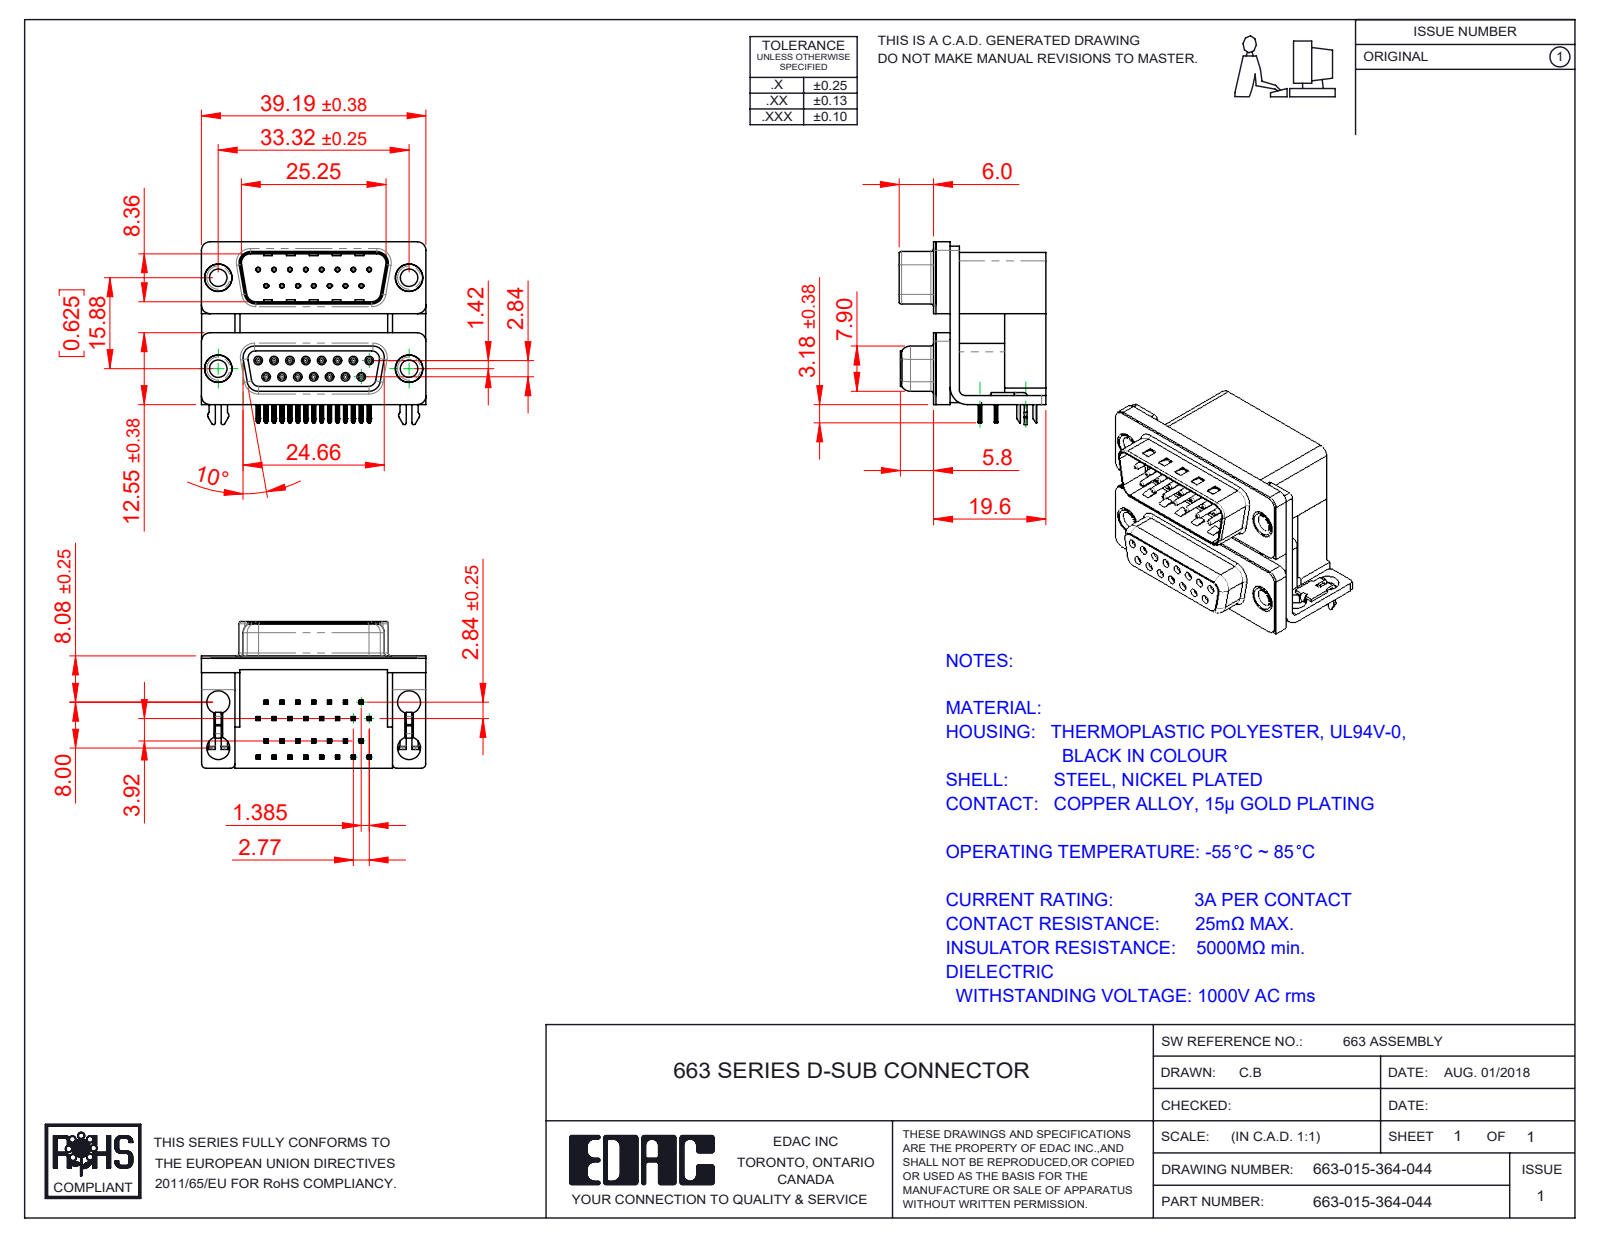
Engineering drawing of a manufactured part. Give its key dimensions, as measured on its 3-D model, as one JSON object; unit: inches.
{"part_name": "663 Contact Bottom Upper_L; 663 Contact Top Lower; 663 Thru Hole Rivet; 663 Housing Spacer_15 Contacts L (+8 more)", "step_written_by": "SolidWorks 2020 (CONFIG_CONTROL_DESIGN)", "units": "inches", "bodies": {"solids": 43, "faces": 3936, "planar": 2093, "cylindrical": 1008, "other": 835}, "overall_size": [1.543, 1.257, 1.008], "volume_in3": 0.888, "surface_area_in2": 25.22, "round_holes": [[0.031, 30], [0.014, 15], [0.035, 15], [0.157, 8], [0.12, 4], [0.138, 4], [0.189, 4], [0.197, 4]], "round_bosses_or_shafts": [[0.047, 15], [0.03, 15], [0.193, 4], [0.187, 4], [0.152, 4]], "partial_cylinders_radius": [[0.004, 121], [0.01, 66], [0.006, 60], [0.005, 30], [0.014, 30], [0.02, 16], [0.059, 16], [0.013, 15]], "face_to_face_distances": [0.016, 0.756, 0.657, 0.098, 0.421, 0.283, 0.472, 0.374, 0.114, 0.772], "hole_center_spacings": [0.124, 0.635, 0.109, 0.662, 0.218, 0.327, 0.625, 0.706]}
